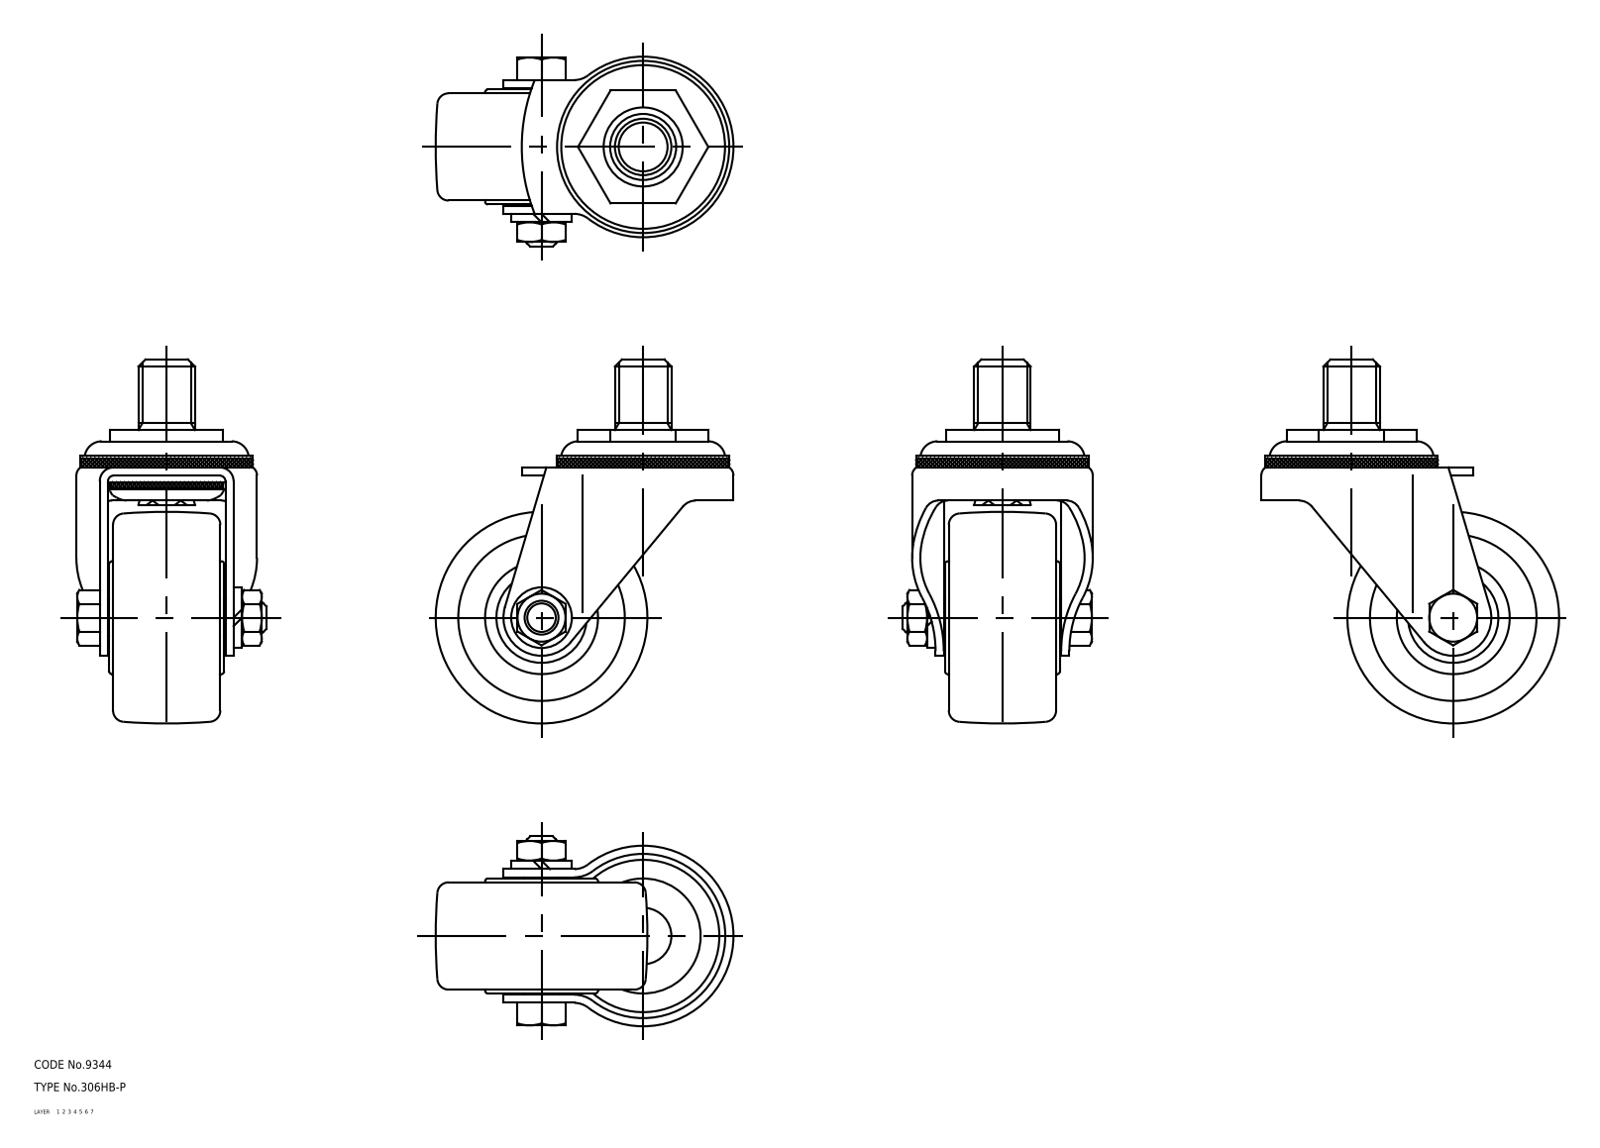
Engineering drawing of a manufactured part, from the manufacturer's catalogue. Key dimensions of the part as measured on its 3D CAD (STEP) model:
Part name (STEP PRODUCT): 67122581; 67122594; 67122607; 67122620
STEP written by: CADfix (AUTOMOTIVE_DESIGN)
Units: millimetres
Bodies: 4 solids, 208 faces (0 planar, 0 cylindrical, 208 other)
Overall size (bounding box): 129 × 105.5 × 67.3
Volume: 236 016 mm³ · Surface area: 54 274 mm²
